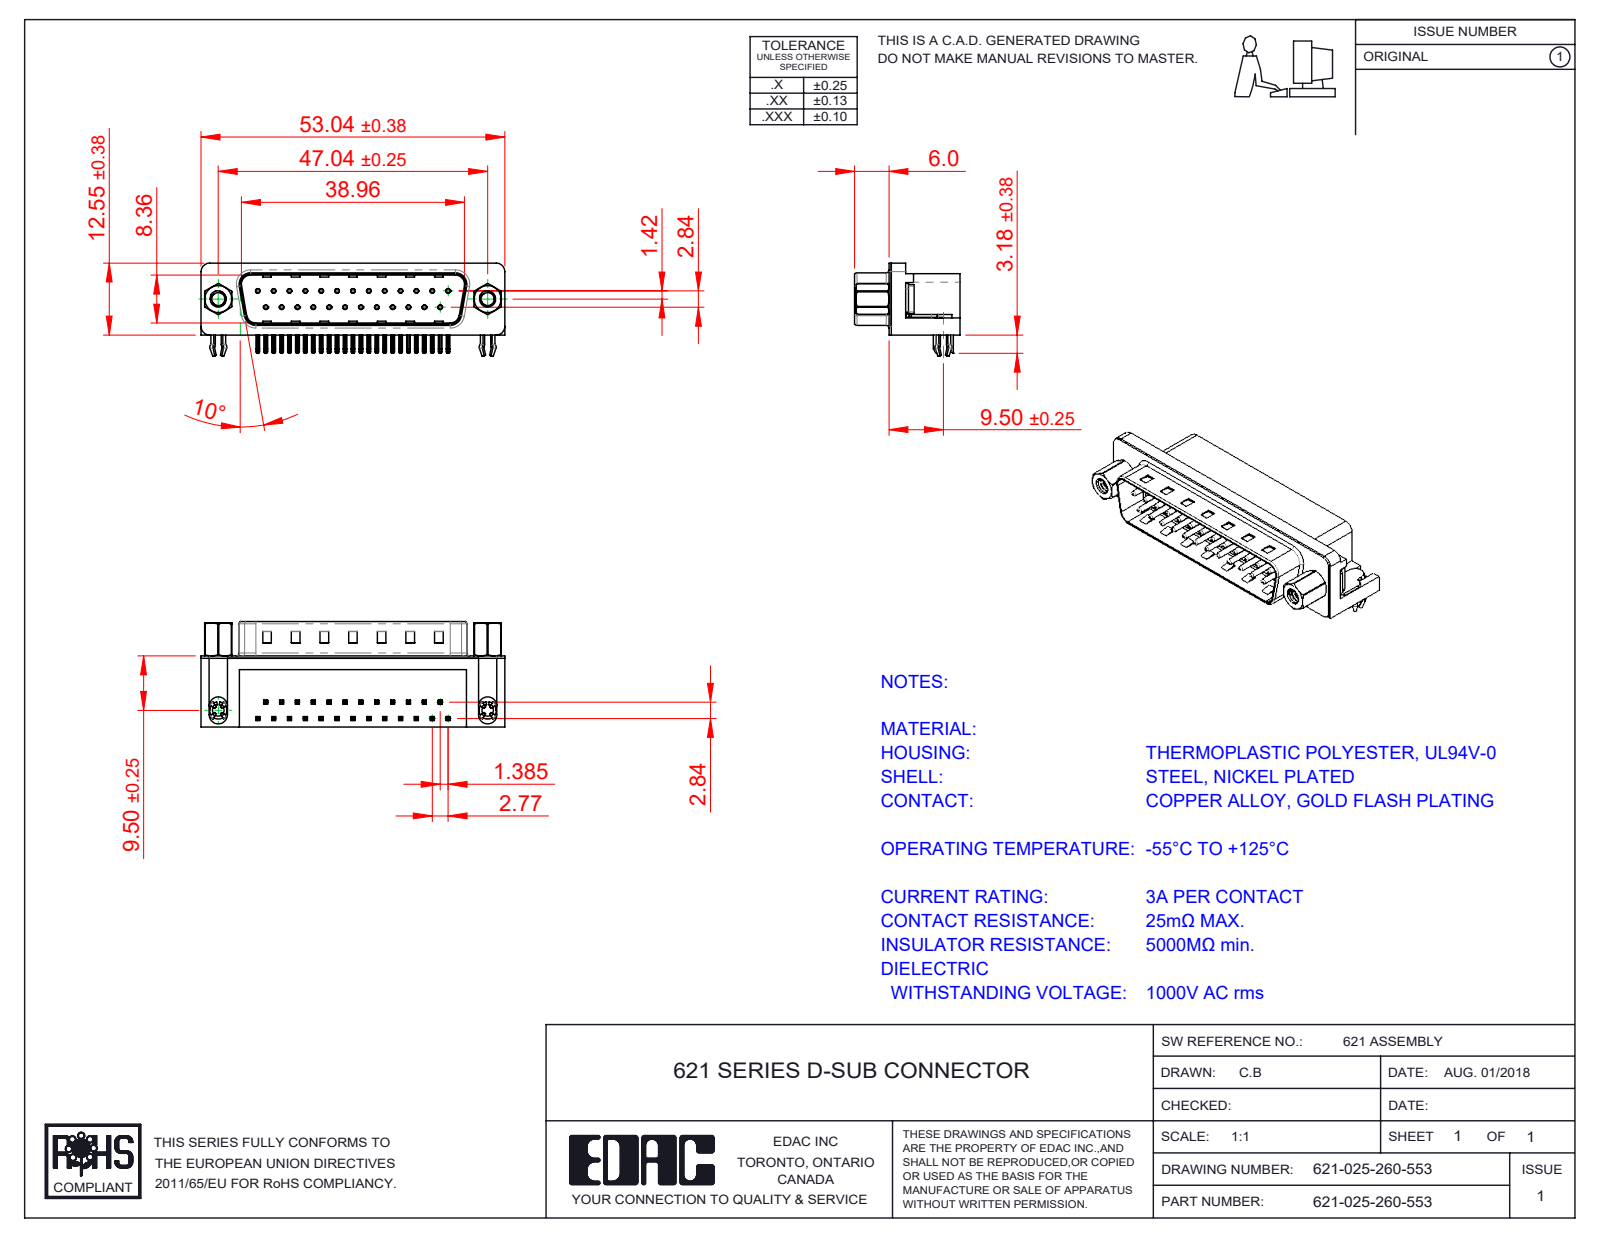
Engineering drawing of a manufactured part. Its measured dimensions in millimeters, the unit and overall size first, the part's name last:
Units: millimetres
Overall size (bounding box): 53.04 × 18.4 × 15.73
Round holes (diameter × count): ⌀0.35 ×25, ⌀0.8 ×25, ⌀2.26 ×4, ⌀2.29 ×2, ⌀4 ×2, ⌀4.8 ×2, ⌀5 ×2
Round bosses / shafts (diameter × count): ⌀0.75 ×25, ⌀4.9 ×2, ⌀4.75 ×2, ⌀3.9 ×2, ⌀3.26 ×2, ⌀2.79 ×2
Partial cylindrical surfaces — rounded edges, fillets, slot ends (radius × count): R0.25 ×108, R0.12 ×50, R1 ×16, R0.5 ×9, R1.6 ×8, R1.5 ×7, R0.9 ×4, R2 ×4
Main face-to-face distances: 0.4, 12, 10.35, 2.1, 8.76, 10.46, 1.7, 10.86, 12.4, 9
Hole centre spacings: 3.16, 2.77, 5.54, 8.31, 11.08, 13.85, 16.62, 5.03
Volume: 6 572 mm³ · Surface area: 8 245 mm²
Bodies: 33 solids, 2419 faces (1427 planar, 743 cylindrical, 249 other)
Part name (STEP PRODUCT): 621 Housing_25 Socket; 621 4-40 Threaded Rivet; 621 4-40 Threaded Board Mount; 621-025-260-553 (+4 more)
STEP written by: SolidWorks 2016 (CONFIG_CONTROL_DESIGN)
